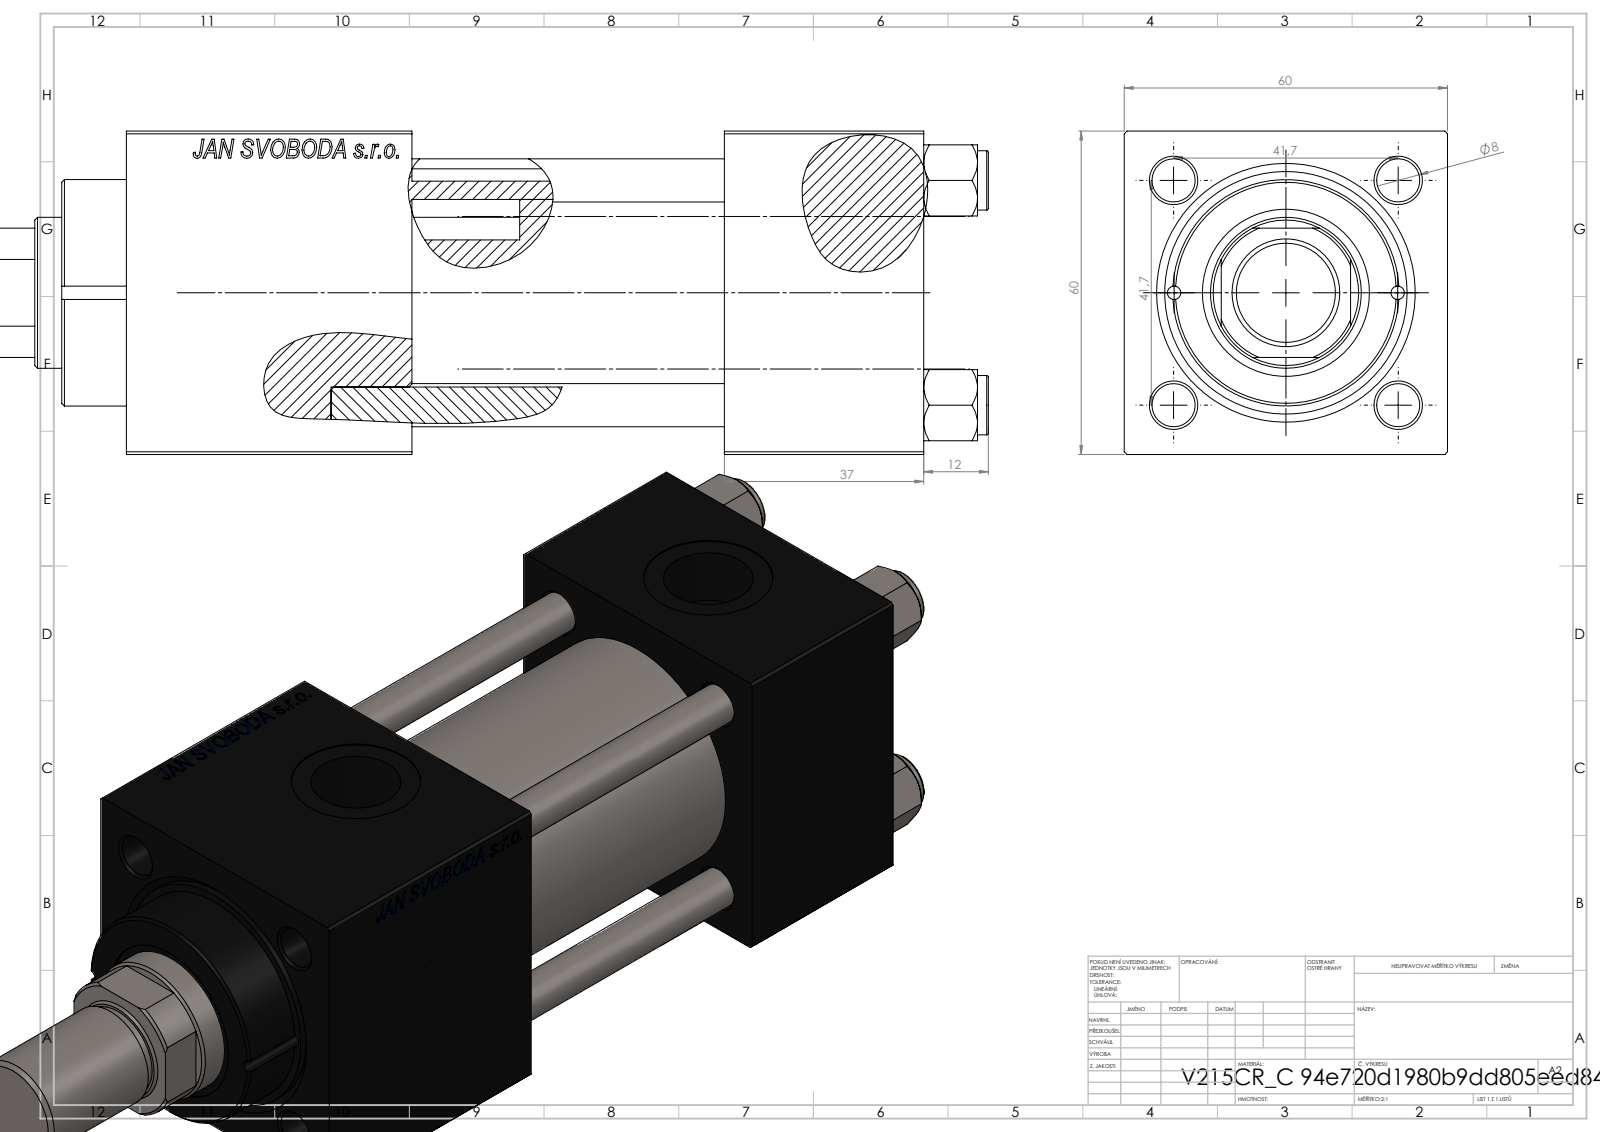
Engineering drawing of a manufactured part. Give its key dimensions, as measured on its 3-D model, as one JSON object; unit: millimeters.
{"part_name": "V215_VC_A; V215CR_C_TYCINKA; NUT_M5_C; V215CR_C_Body (+2 more)", "step_written_by": "SolidWorks 2019 (CONFIG_CONTROL_DESIGN)", "units": "millimeters", "bodies": {"solids": 12, "faces": 1169, "planar": 532, "cylindrical": 95, "other": 542}, "overall_size": [213, 60, 60], "volume_mm3": 432618, "surface_area_mm2": 113992, "round_holes": [[8, 4], [2.5, 2], [7, 2], [16.66, 2], [24, 2], [18.5, 1], [28, 1], [31, 1], [40, 1], [45, 1]], "round_bosses_or_shafts": [[11, 4], [46, 1], [42, 1], [20, 1], [18, 1]], "partial_cylinders_radius": [[13.5, 1]], "face_to_face_distances": [60, 37, 58, 53, 95, 119.3, 82.3, 24.3, 148, 111], "hole_center_spacings": [20.85, 29.49, 41.7, 46.53, 20.75, 58.97, 41.5, 92.5]}
